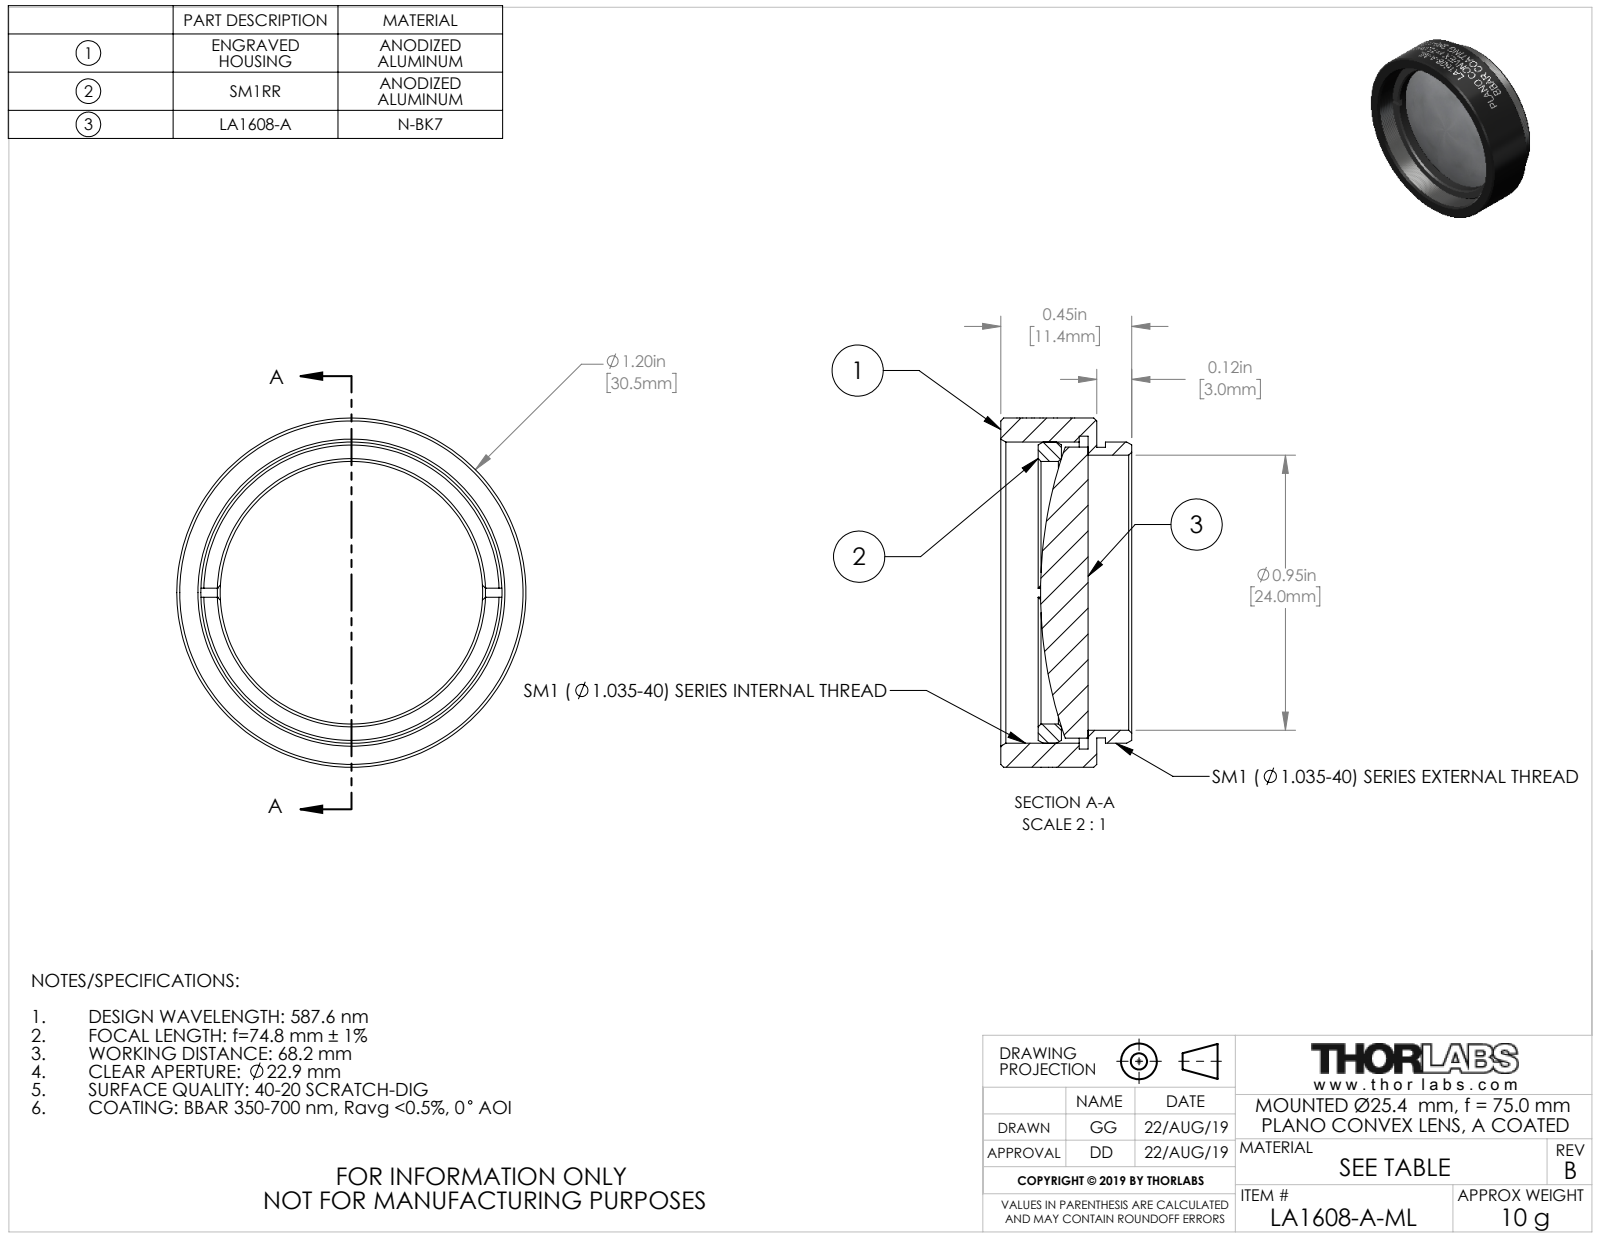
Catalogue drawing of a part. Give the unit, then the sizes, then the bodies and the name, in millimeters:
Units: millimetres
Overall size (bounding box): 30.48 × 30.48 × 11.43
Round holes (diameter × count): ⌀22.91 ×1, ⌀24 ×1, ⌀27.3 ×1
Round bosses / shafts (diameter × count): ⌀30.48 ×1, ⌀26.29 ×1, ⌀25.4 ×1, ⌀25.37 ×1
Main face-to-face distances: 0.76, 8.38, 7.62, 3.08, 2.32, 5.3, 5.11, 4.35, 2.03, 3.27
Volume: 3 640 mm³ · Surface area: 4 326 mm²
Bodies: 3 solids, 152 faces (20 planar, 108 cylindrical, 24 other)
Part name (STEP PRODUCT): 24427-E0W
STEP written by: SolidWorks 2018 (CONFIG_CONTROL_DESIGN)
